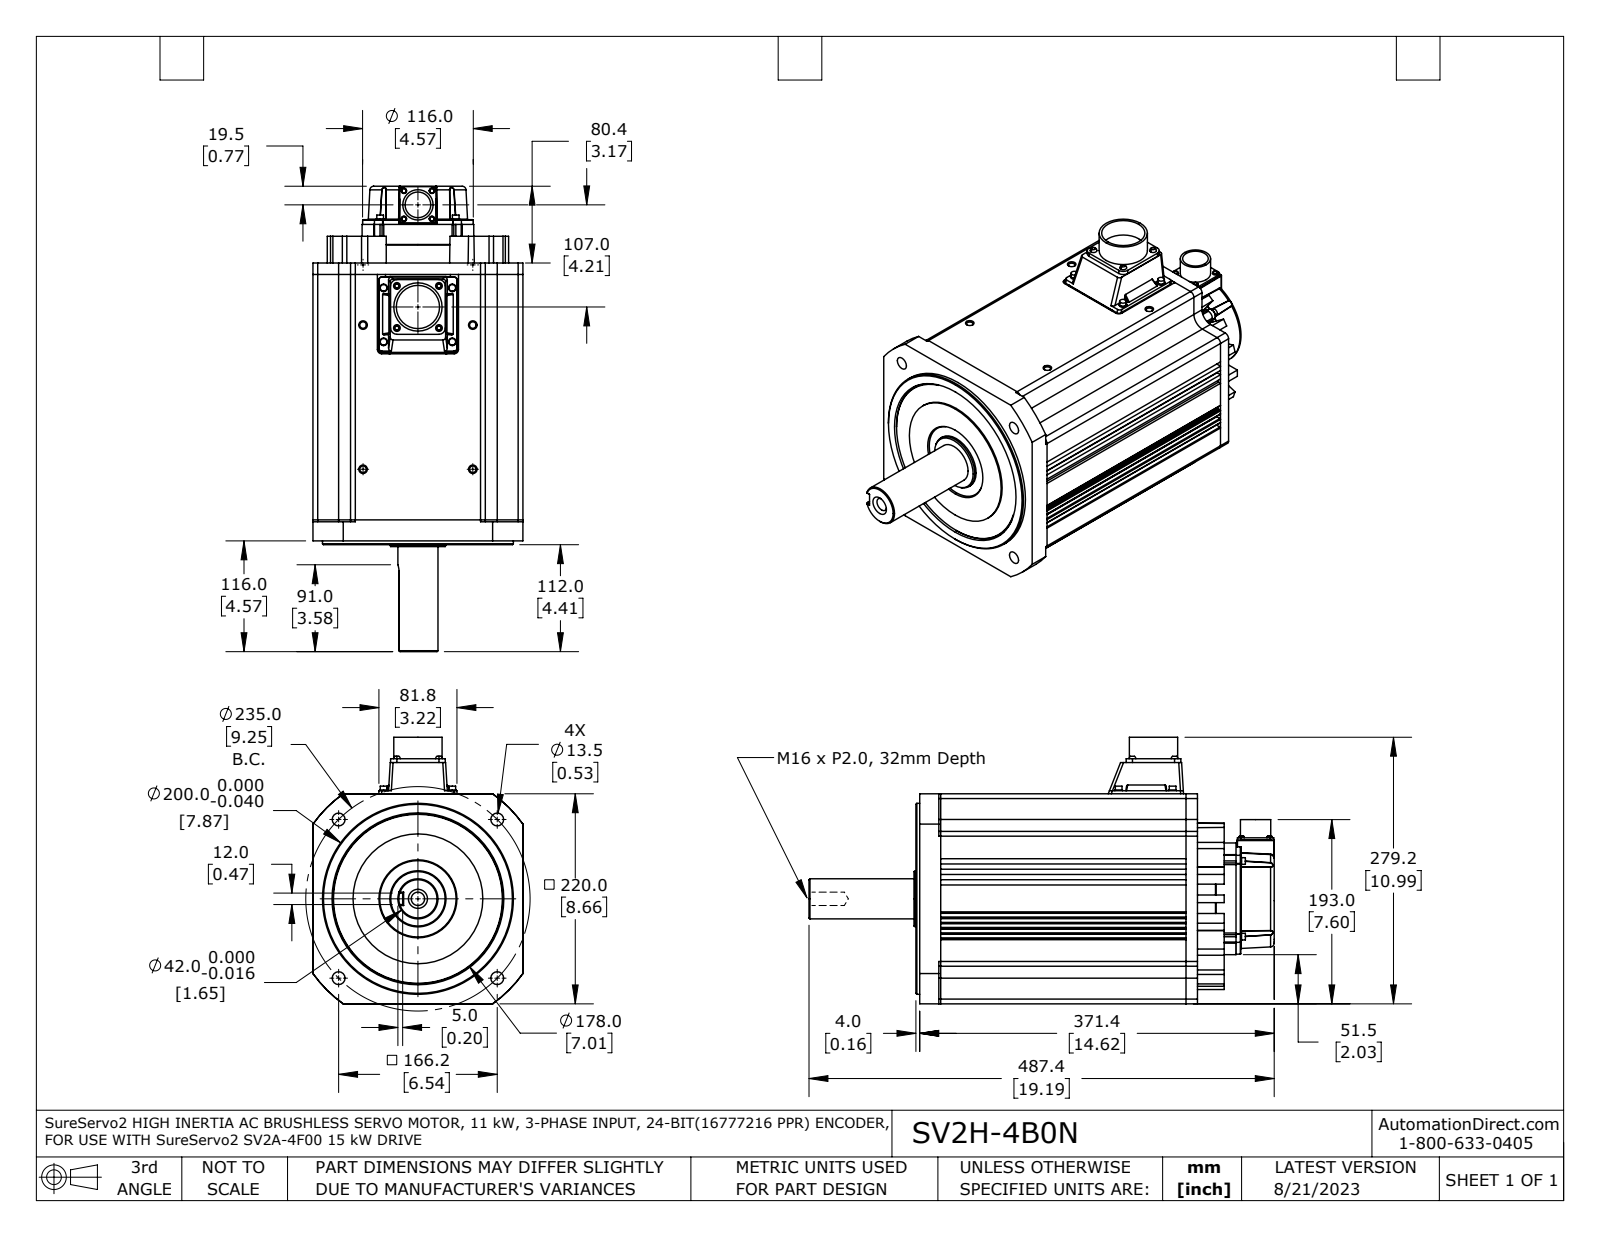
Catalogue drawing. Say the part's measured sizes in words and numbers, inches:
The part is named "SV2H-4B0N cut1a fxt". Its 3-D file was written by "SolidWorks 2021 (AUTOMOTIVE_DESIGN)". It is 1 solid with 833 faces: 350 planar, 257 cylindrical and 226 other. Overall it measures 19.189 by 10.992 by 8.661 inches. Its volume is 827.7 cubic inches and its surface area 803.1 square inches. Round holes: 4 of diameter 0.169, 4 of diameter 0.181, 4 of diameter 0.268, 4 of diameter 0.531, 1 of diameter 0.551, 1 of diameter 1.058, 1 of diameter 1.783, 1 of diameter 7.087. Round bosses or shafts: 8 of diameter 0.315, 8 of diameter 0.276, 4 of diameter 0.157, 1 of diameter 7.874, 1 of diameter 7.008, 1 of diameter 5.354, 1 of diameter 4.551, 1 of diameter 2.315. Partial cylindrical surfaces (rounded edges, fillets, slot ends): 44 of radius 0.02, 24 of radius 0.031, 18 of radius 0.197, 16 of radius 0.118, 8 of radius 0.157, 4 of radius 0.039, 4 of radius 0.217, 4 of radius 0.26. The main face-to-face distances are 8.661, 1.551, 7.11, 0.217, 0.433, 5.559, 0.157, 2.441, 2.657, 0.65. The hole center spacings are 4.626, 6.543, 1.093, 1.621, 1.752, 2.019, 2.224, 2.383.
